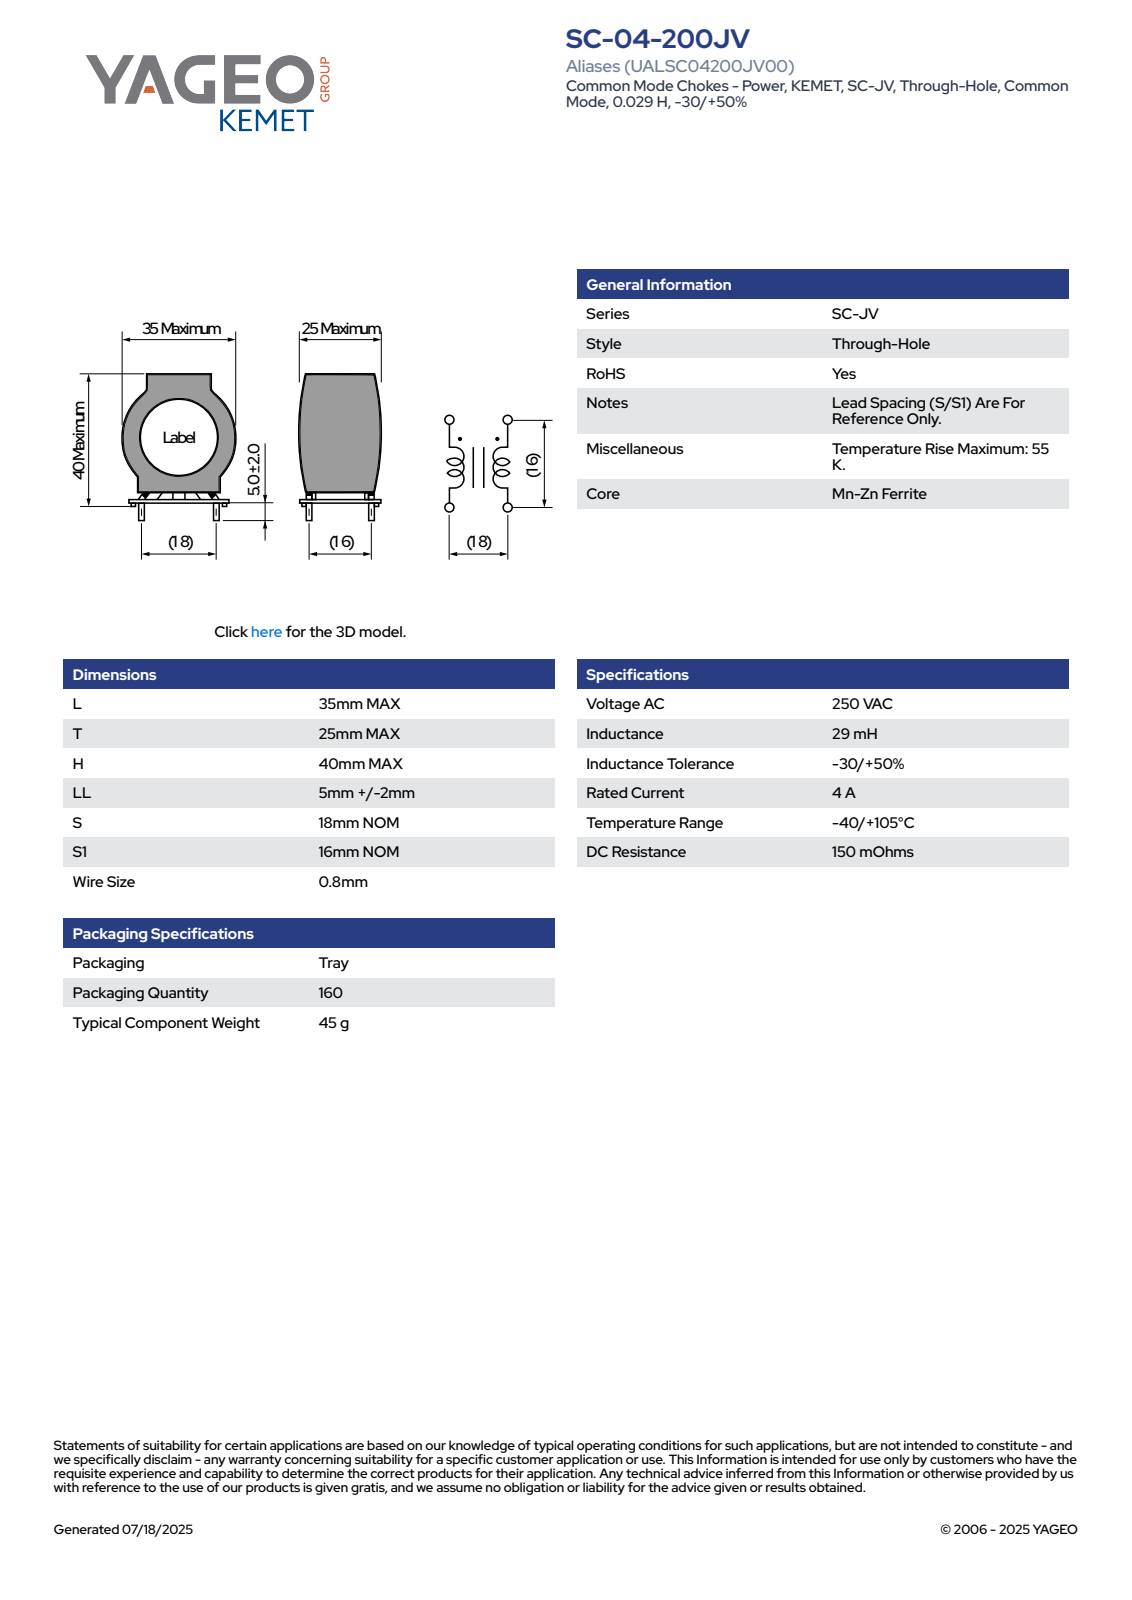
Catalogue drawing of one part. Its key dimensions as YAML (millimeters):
part_name: "SC-04-200JV"
step_written_by: "SolidWorks 2018 (AUTOMOTIVE_DESIGN)"
units: millimeters
bodies: {solids: 1, faces: 479, planar: 188, cylindrical: 157, other: 134}
overall_size: [45.02, 35, 25]
volume: 17594
surface_area: 13203
round_holes:
  - {diameter: 1, count: 4}
round_bosses_or_shafts:
  - {diameter: 0.8, count: 8}
  - {diameter: 1, count: 4}
partial_cylinders:
  - {radius: 0.5, count: 20}
  - {radius: 0.4, count: 16}
  - {radius: 1.5, count: 8}
  - {radius: 1, count: 6}
  - {radius: 2, count: 6}
  - {radius: 5, count: 6}
  - {radius: 4.5, count: 5}
  - {radius: 0.7, count: 4}
face_to_face_distances: [0.5, 24.5, 3, 2.5, 21.5, 22, 24, 25, 19, 2.4]
hole_center_spacings: [16, 18, 24.08]
